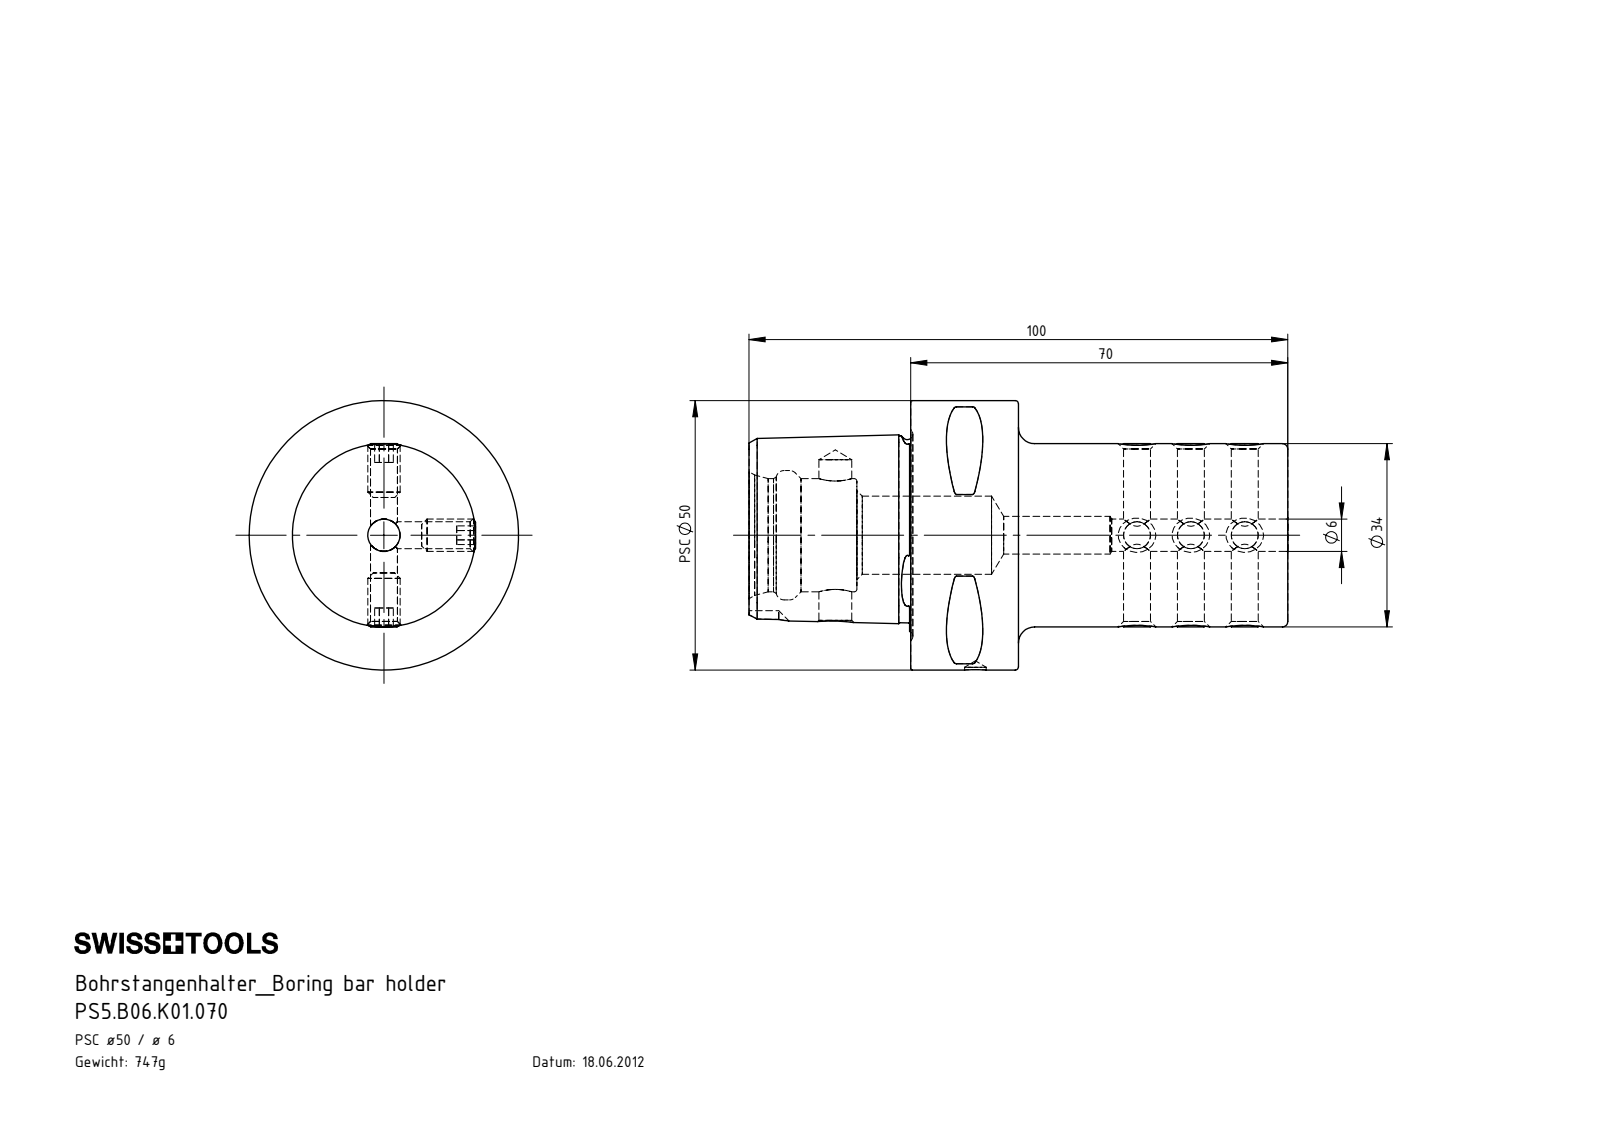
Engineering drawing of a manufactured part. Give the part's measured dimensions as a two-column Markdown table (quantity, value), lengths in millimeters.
| quantity | value |
| --- | --- |
| part name | PS5.B06.K01.070; PS5-B06.K01.070_A; ISO 4026 - M6 x 10_PreviewCfg |
| STEP written by | SolidWorks 2017 (AUTOMOTIVE_DESIGN) |
| units | millimeters |
| bodies | 10 solids, 306 faces (101 planar, 70 cylindrical, 135 other) |
| overall size | 100 × 50 × 50 |
| volume | 97 024 mm³ |
| surface area | 23 114 mm² |
| round holes (diameter × count) | 5 × 6, 4 × 1, 6 × 1, 6.1 × 1, 7 × 1, 14.5 × 1, 21 × 1, 24 × 1 |
| round bosses / shafts (diameter × count) | 6 × 6, 50 × 1, 34 × 1 |
| partial cylindrical surfaces (radius × count) | 0.5 × 8, 4 × 1 |
| main face-to-face distances | 50, 20, 70, 30, 100, 10, 19.18, 3, 5, 44.4 |
| hole center spacings | 10, 20, 26, 30, 40, 50, 56, 66 |
